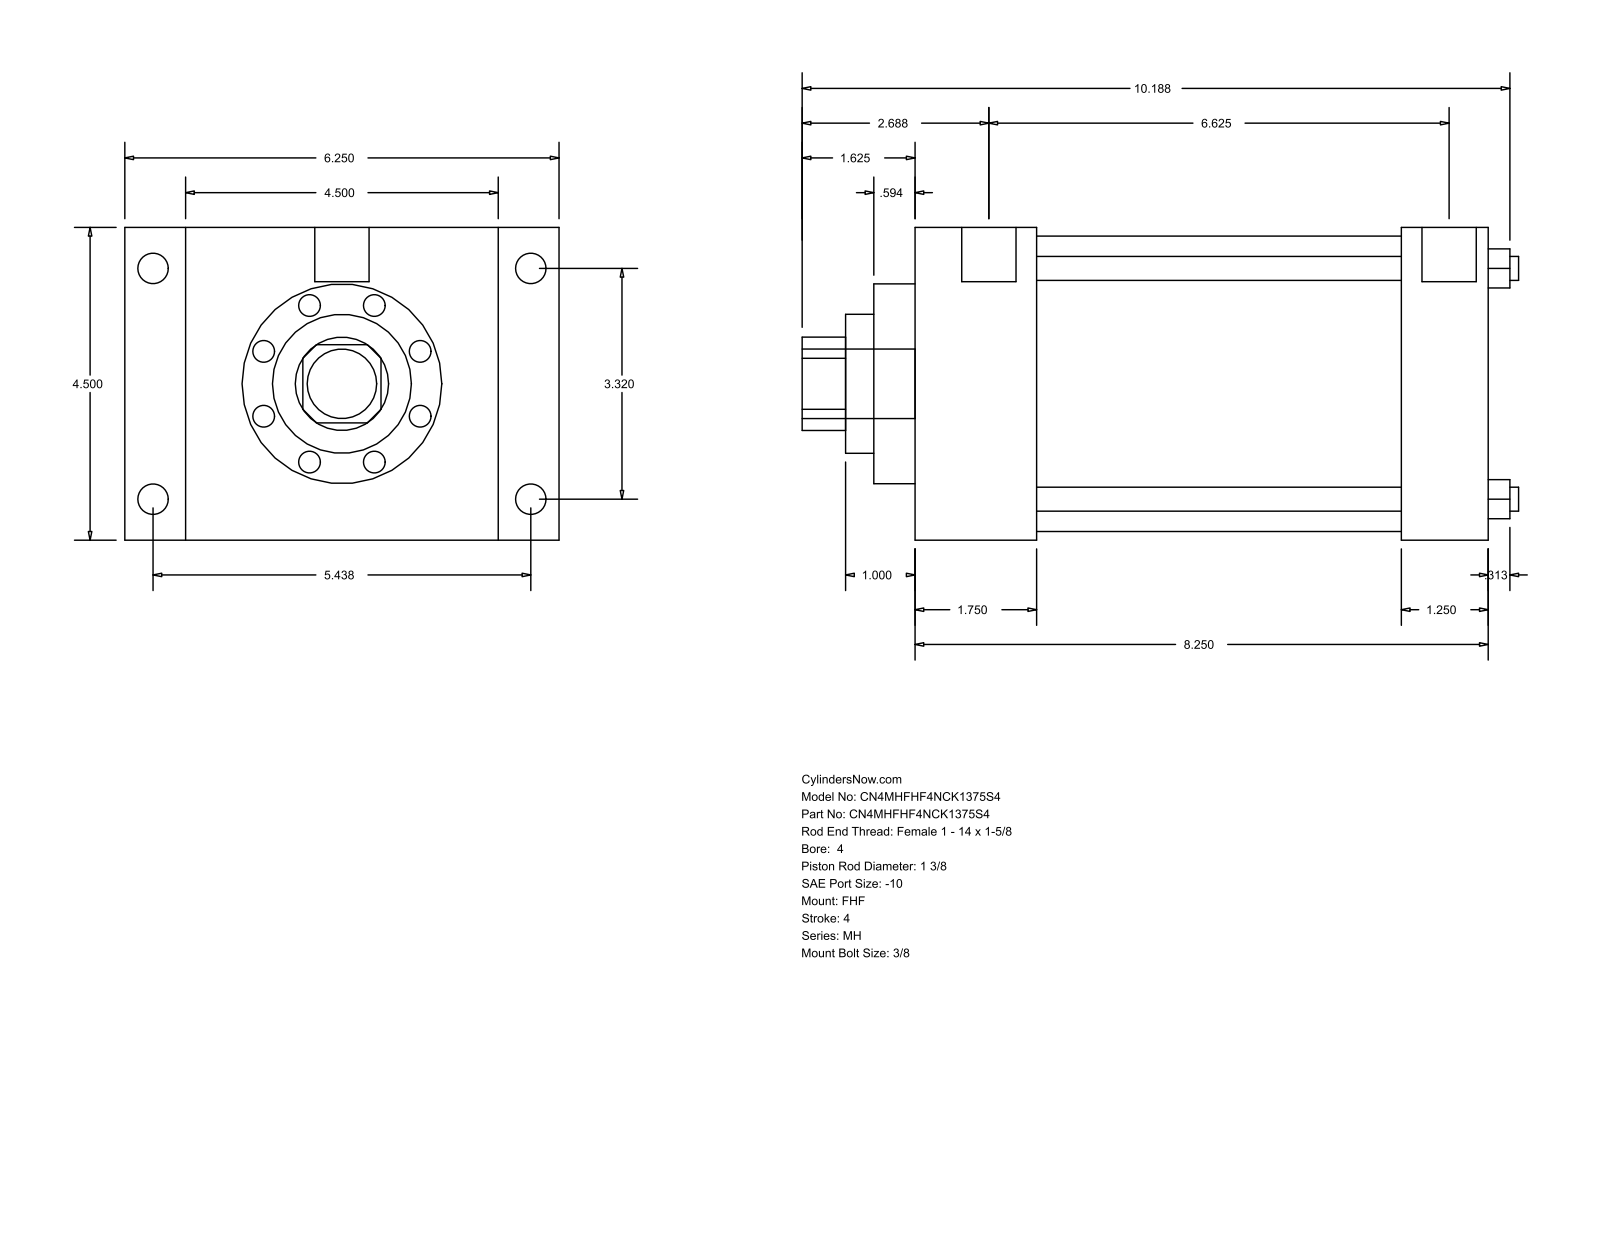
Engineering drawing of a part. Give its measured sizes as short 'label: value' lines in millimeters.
name: MH_FHF__0400_1.375
written by: GSSL Pune (CONFIG_CONTROL_DESIGN)
unit: mm
bodies: 0 solids, 90 faces (61 planar, 29 cylindrical, 0 other)
size: 261.94 × 158.75 × 114.3
holes: 4× ⌀8.76, 1× ⌀34.92, 1× ⌀50.8, 1× ⌀73.03, 1× ⌀107.95
bosses: 4× ⌀11.13, 4× ⌀8.73, 2× ⌀19.84, 1× ⌀25.4
rounds: 1× R17.06
face distances: 114.3, 209.55, 44.45, 165.1, 22.23, 136.53, 158.76, 177.8, 133.35, 31.75
hole spacings: 59.62, 84.32, 119.25
